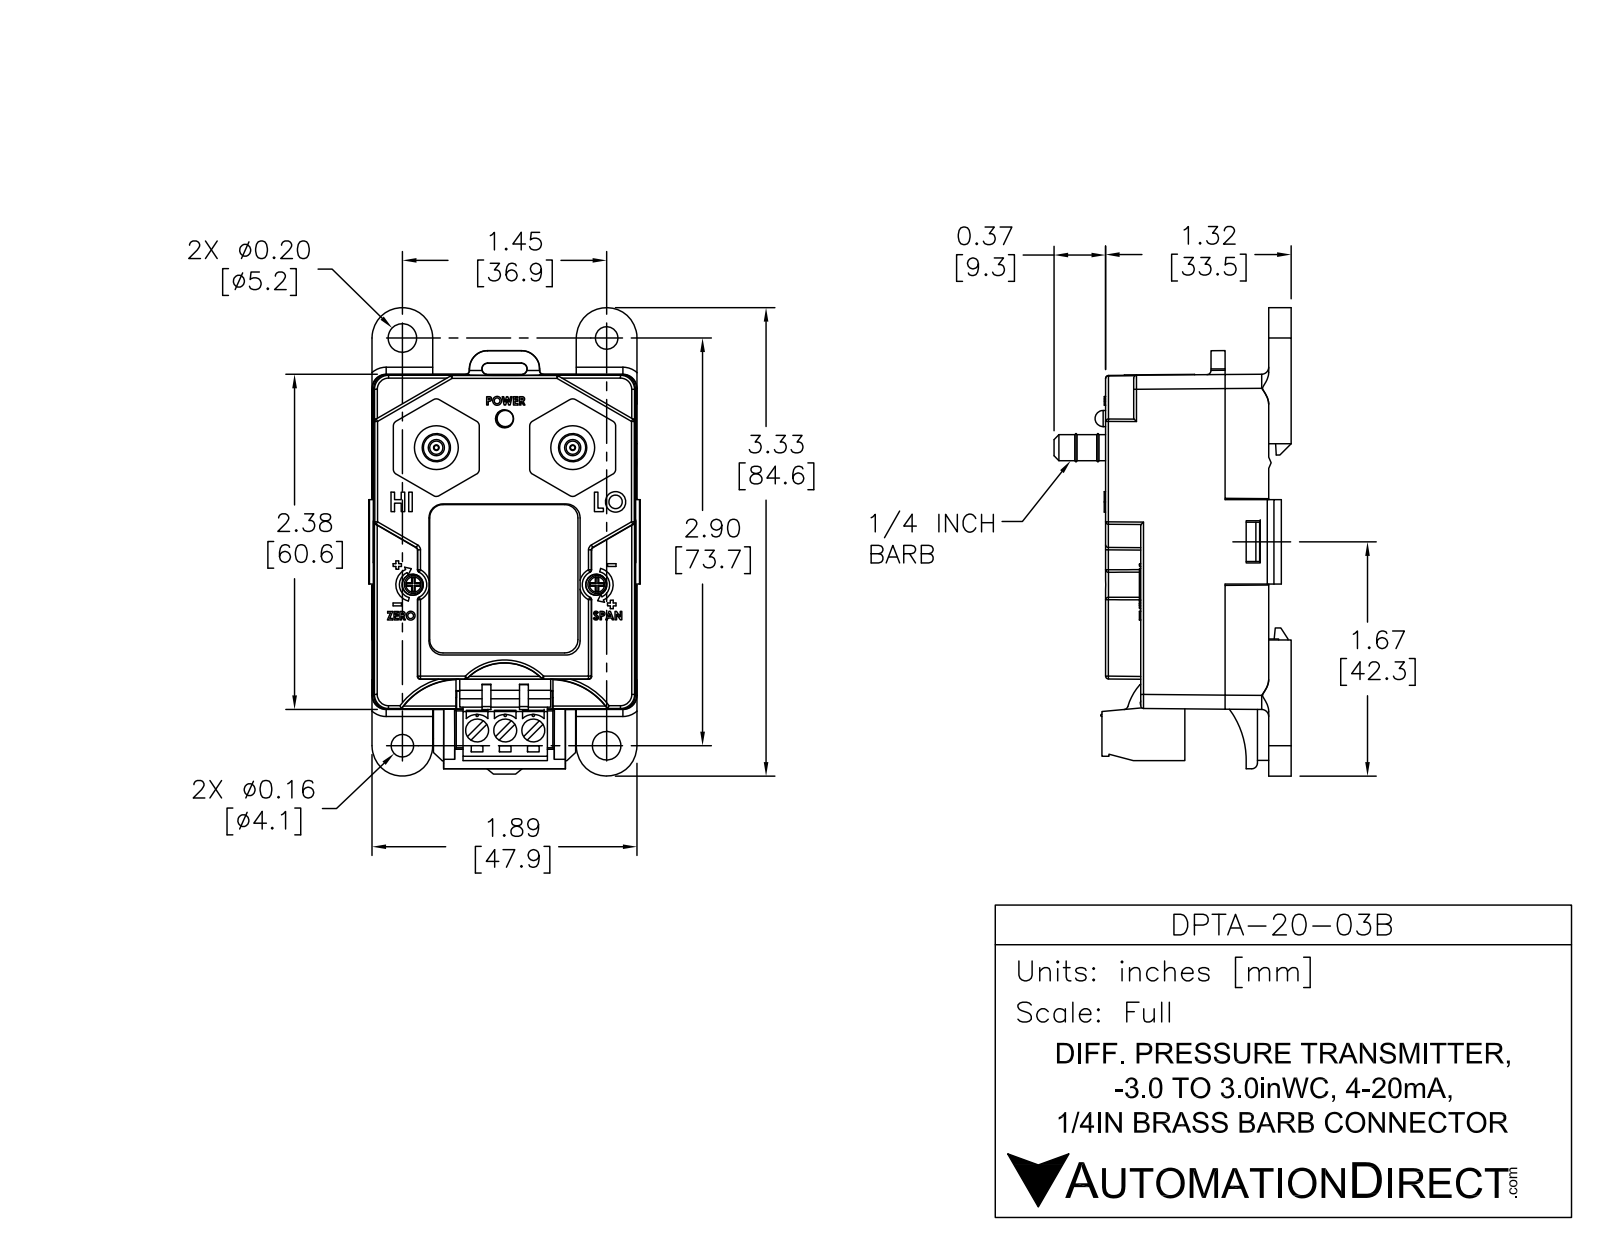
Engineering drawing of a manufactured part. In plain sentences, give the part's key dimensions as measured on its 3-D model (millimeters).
The part is named "DPTA-20-03B". Its 3-D file was written by "SolidWorks 2013 (AUTOMOTIVE_DESIGN)". It is 11 solids with 506 faces: 354 planar, 134 cylindrical and 18 other. Overall it measures 85.01 by 49.76 by 43.1 millimeters. Its volume is 29 684 cubic millimeters and its surface area 34 743 square millimeters. Round holes: 7 of diameter 4, 2 of diameter 2.5, 2 of diameter 5.12, 1 of diameter 3.1. Round bosses or shafts: 3 of diameter 5, 3 of diameter 3.5, 3 of diameter 3.5, 2 of diameter 8, 2 of diameter 4.75, 1 of diameter 3. Partial cylindrical surfaces (rounded edges, fillets, slot ends): 12 of radius 3, 4 of radius 2, 4 of radius 5.5, 2 of radius 0.99, 2 of radius 1.06, 2 of radius 1.12, 2 of radius 2.38, 2 of radius 3.25. The main face-to-face distances are 1, 1.9, 4, 29.1, 0.5, 46.9, 5.9, 5, 33.1, 27.2. The hole center spacings are 13.55, 20.73, 23.37, 24.92, 29.43, 34.46, 36.67, 38.22.
